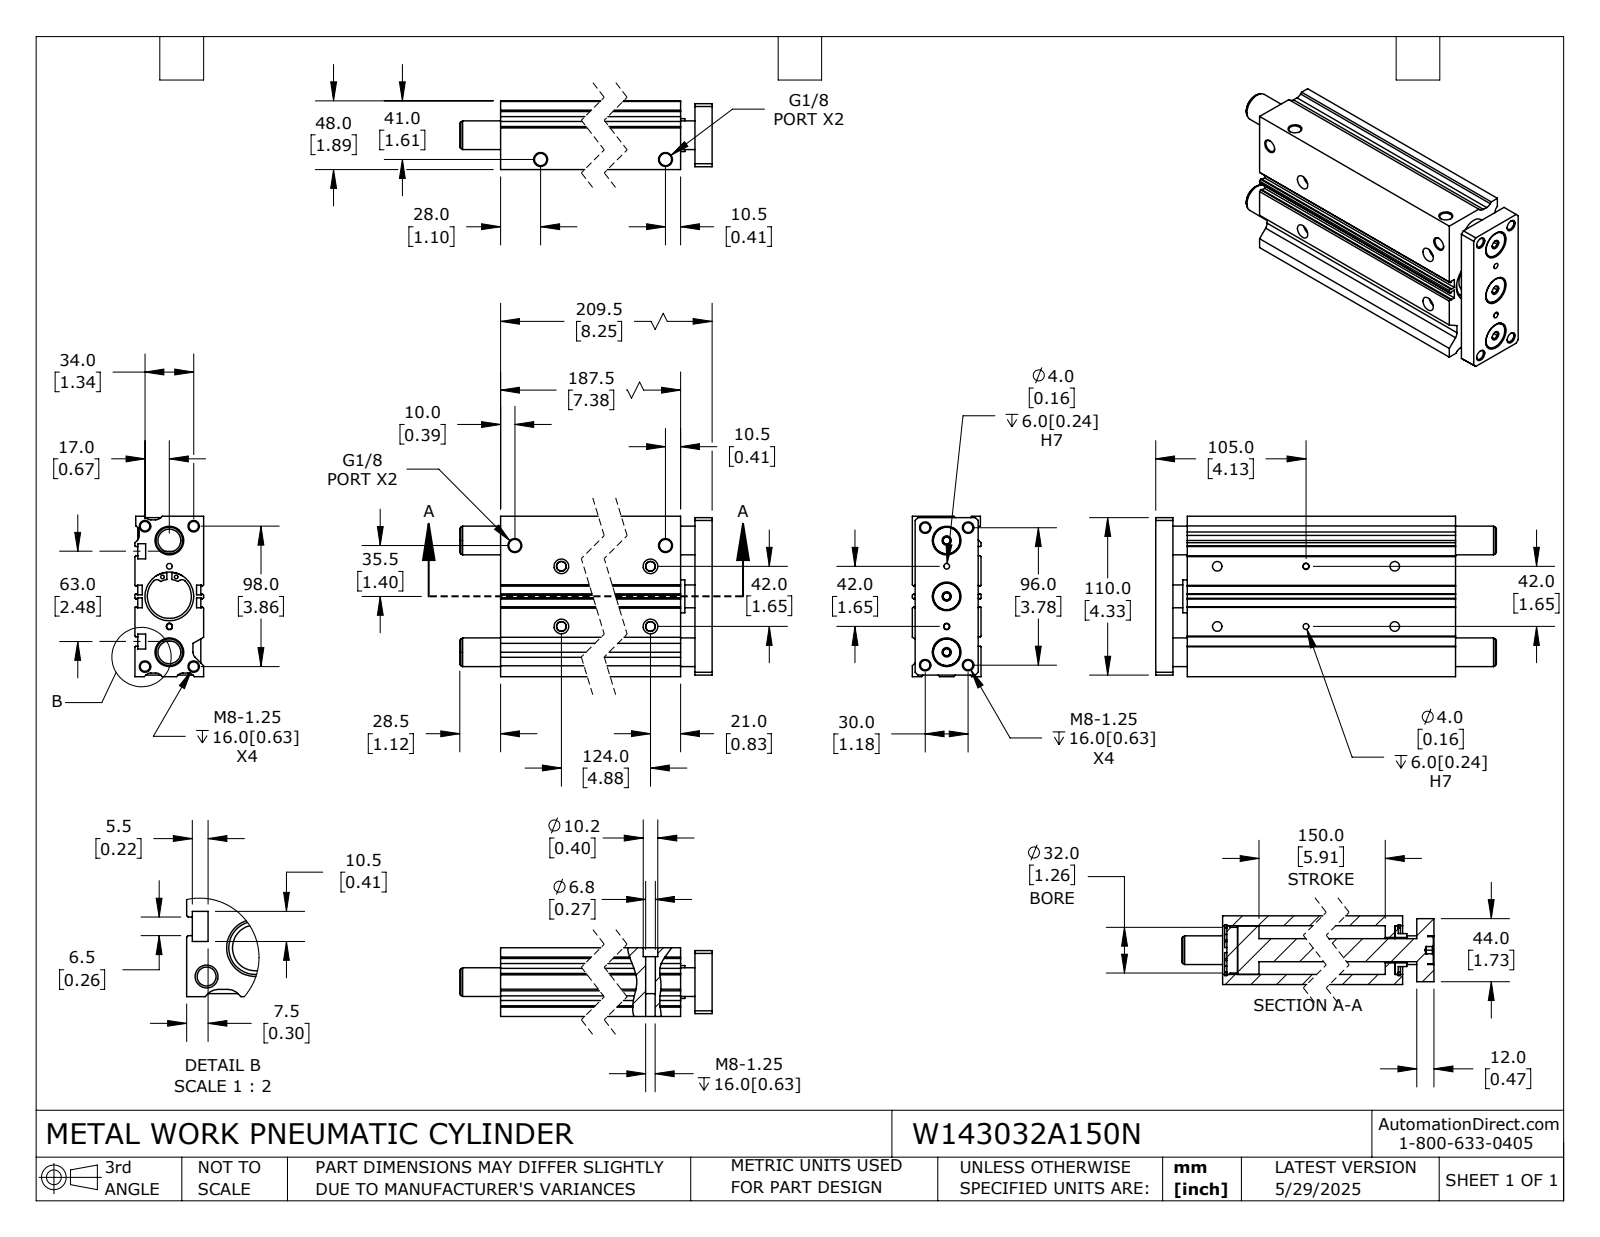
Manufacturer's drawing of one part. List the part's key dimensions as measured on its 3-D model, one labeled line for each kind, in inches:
Part name (STEP PRODUCT): W143032A150N_BODY; W143032A150N_ROD; W143032A150N
STEP written by: SolidWorks 2024 (CONFIG_CONTROL_DESIGN)
Units: inches
Bodies: 6 solids, 394 faces (195 planar, 149 cylindrical, 50 other)
Overall size (bounding box): 9.37 × 4.409 × 1.89
Volume: 53.52 in³ · Surface area: 310.7 in²
Round holes (diameter × count): ⌀0.262 ×12, ⌀0.098 ×4, ⌀0.157 ×4, ⌀0.268 ×4, ⌀0.337 ×4, ⌀0.402 ×4, ⌀0.197 ×3, ⌀0.787 ×3, ⌀0.697 ×1, ⌀1.211 ×1
Round bosses / shafts (diameter × count): ⌀0.748 ×3, ⌀1.406 ×2, ⌀1.339 ×1, ⌀1.26 ×1, ⌀0.906 ×1, ⌀0.63 ×1
Partial cylindrical surfaces — rounded edges, fillets, slot ends (radius × count): R0.197 ×9, R0.079 ×4, R0.118 ×4, R0.507 ×2
Main face-to-face distances: 1.89, 0.295, 0.118, 0.098, 1.693, 0.197, 1.594, 0.079, 0.472, 4.409
Hole centre spacings: 0.088, 0.348, 0.566, 0.689, 0.776, 1.019, 1.216, 1.261
